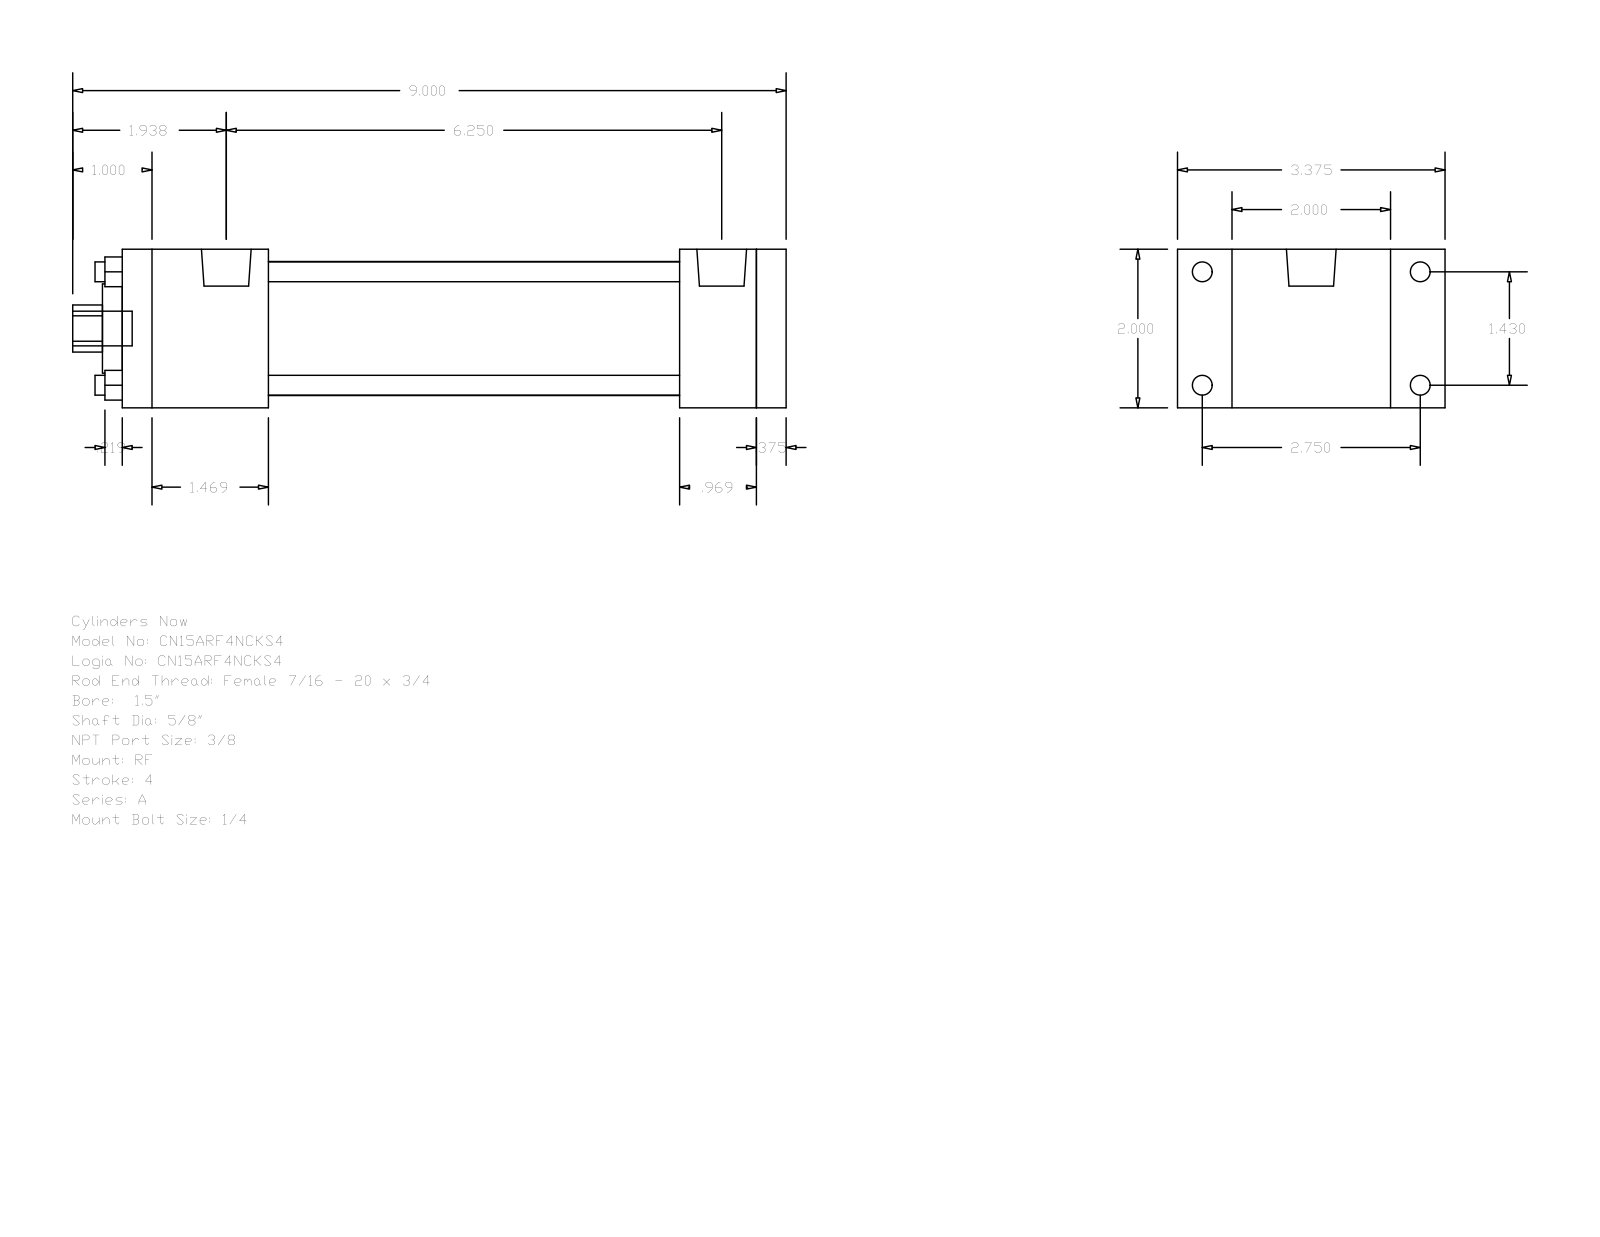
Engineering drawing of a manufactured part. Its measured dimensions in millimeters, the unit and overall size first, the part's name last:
Units: millimetres
Overall size (bounding box): 228.6 × 85.72 × 50.8
Round holes (diameter × count): ⌀6.35 ×4, ⌀15.88 ×1, ⌀28.57 ×1, ⌀42.93 ×1
Round bosses / shafts (diameter × count): ⌀6.35 ×4, ⌀5.56 ×4, ⌀15.93 ×2, ⌀11.11 ×1
Partial cylindrical surfaces — rounded edges, fillets, slot ends (radius × count): R7.54 ×1
Main face-to-face distances: 50.8, 9.53, 212.72, 203.19, 178.59, 24.6, 34.13, 46.83, 131.76, 156.36
Hole centre spacings: 25.68, 36.32, 51.36
Bodies: 0 solids, 92 faces (64 planar, 28 cylindrical, 0 other)
Part name (STEP PRODUCT): A_RF__0150_0.625
STEP written by: GSSL Pune (CONFIG_CONTROL_DESIGN)
